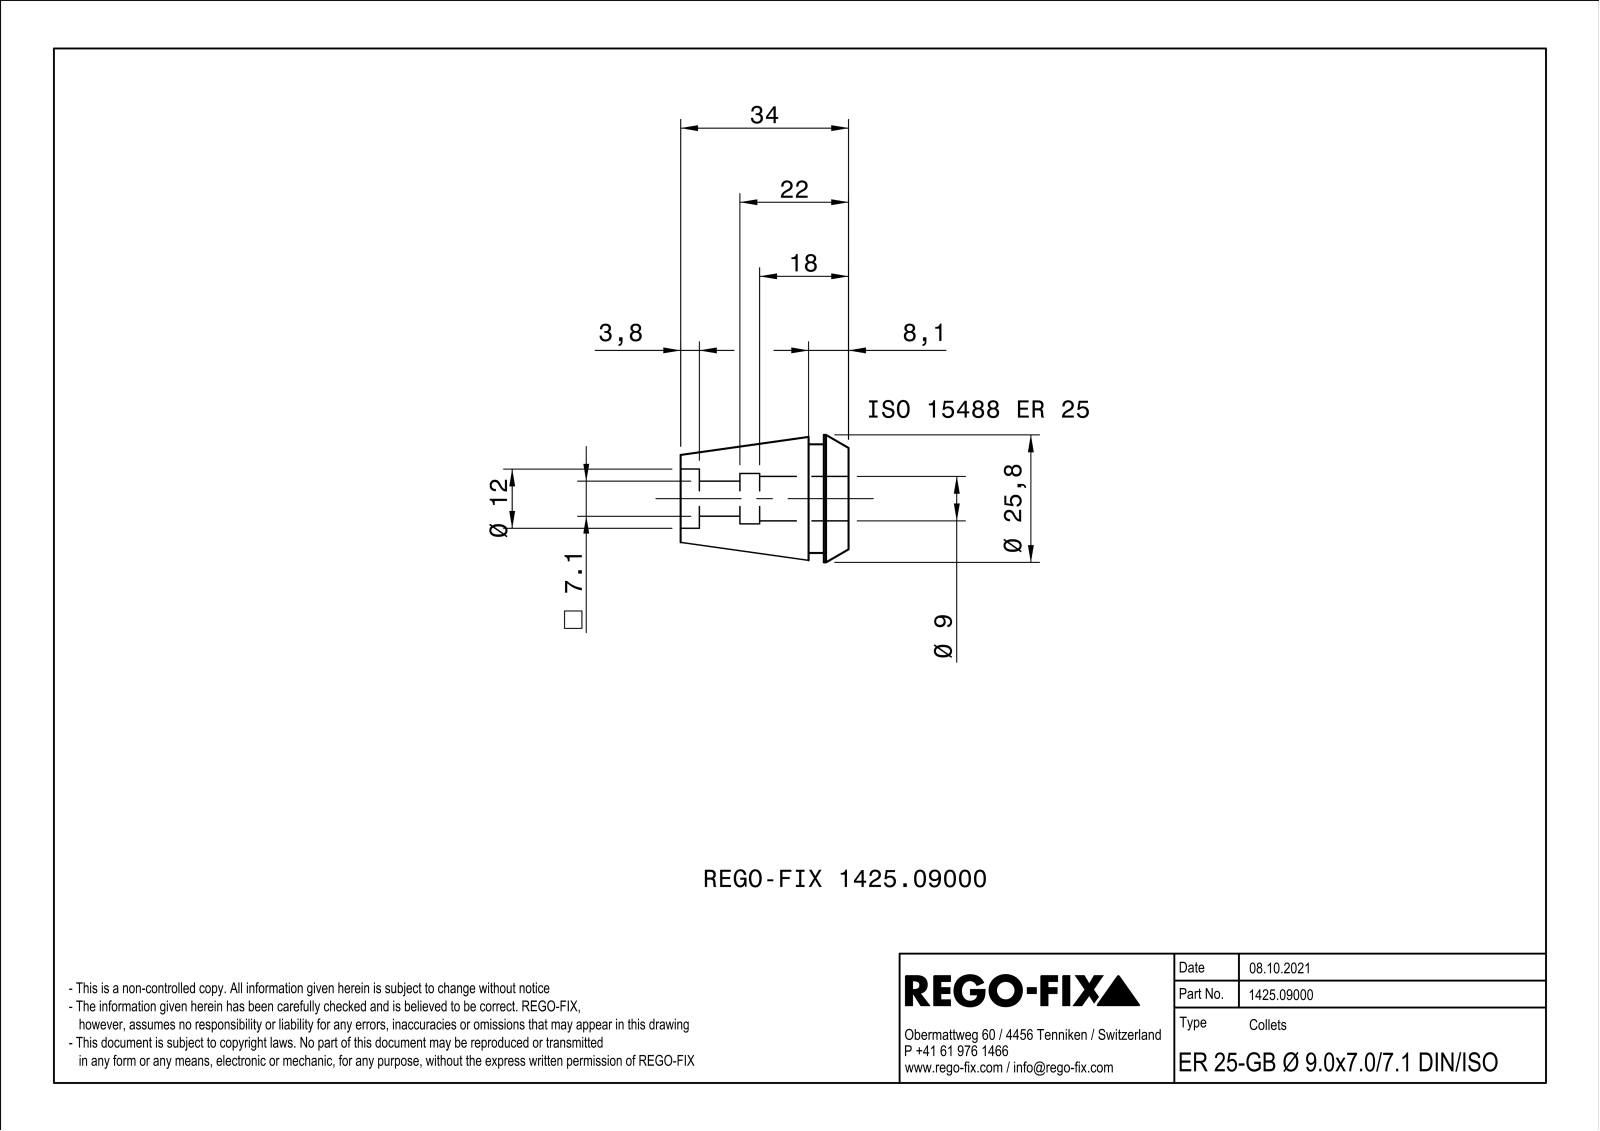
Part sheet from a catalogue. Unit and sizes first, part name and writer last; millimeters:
Units: millimetres
Overall size (bounding box): 34 × 25.79 × 25.79
Round holes (diameter × count): ⌀9 ×1, ⌀10.2 ×1, ⌀12 ×1
Round bosses / shafts (diameter × count): ⌀25.8 ×1, ⌀22 ×1
Partial cylindrical surfaces — rounded edges, fillets, slot ends (radius × count): R4.15 ×1, R4.9 ×1
Main face-to-face distances: 0.8, 5, 3.4, 4.2, 8.1, 3.1, 34, 29, 25.9, 7.6
Volume: 9 100 mm³ · Surface area: 6 622 mm²
Bodies: 1 solid, 160 faces (68 planar, 40 cylindrical, 52 other)
Part name (STEP PRODUCT): NOCUT
STEP written by: SIEMENS PLM Software Solid Edge ST10 (AUTOMOTIVE_DESIGN)
